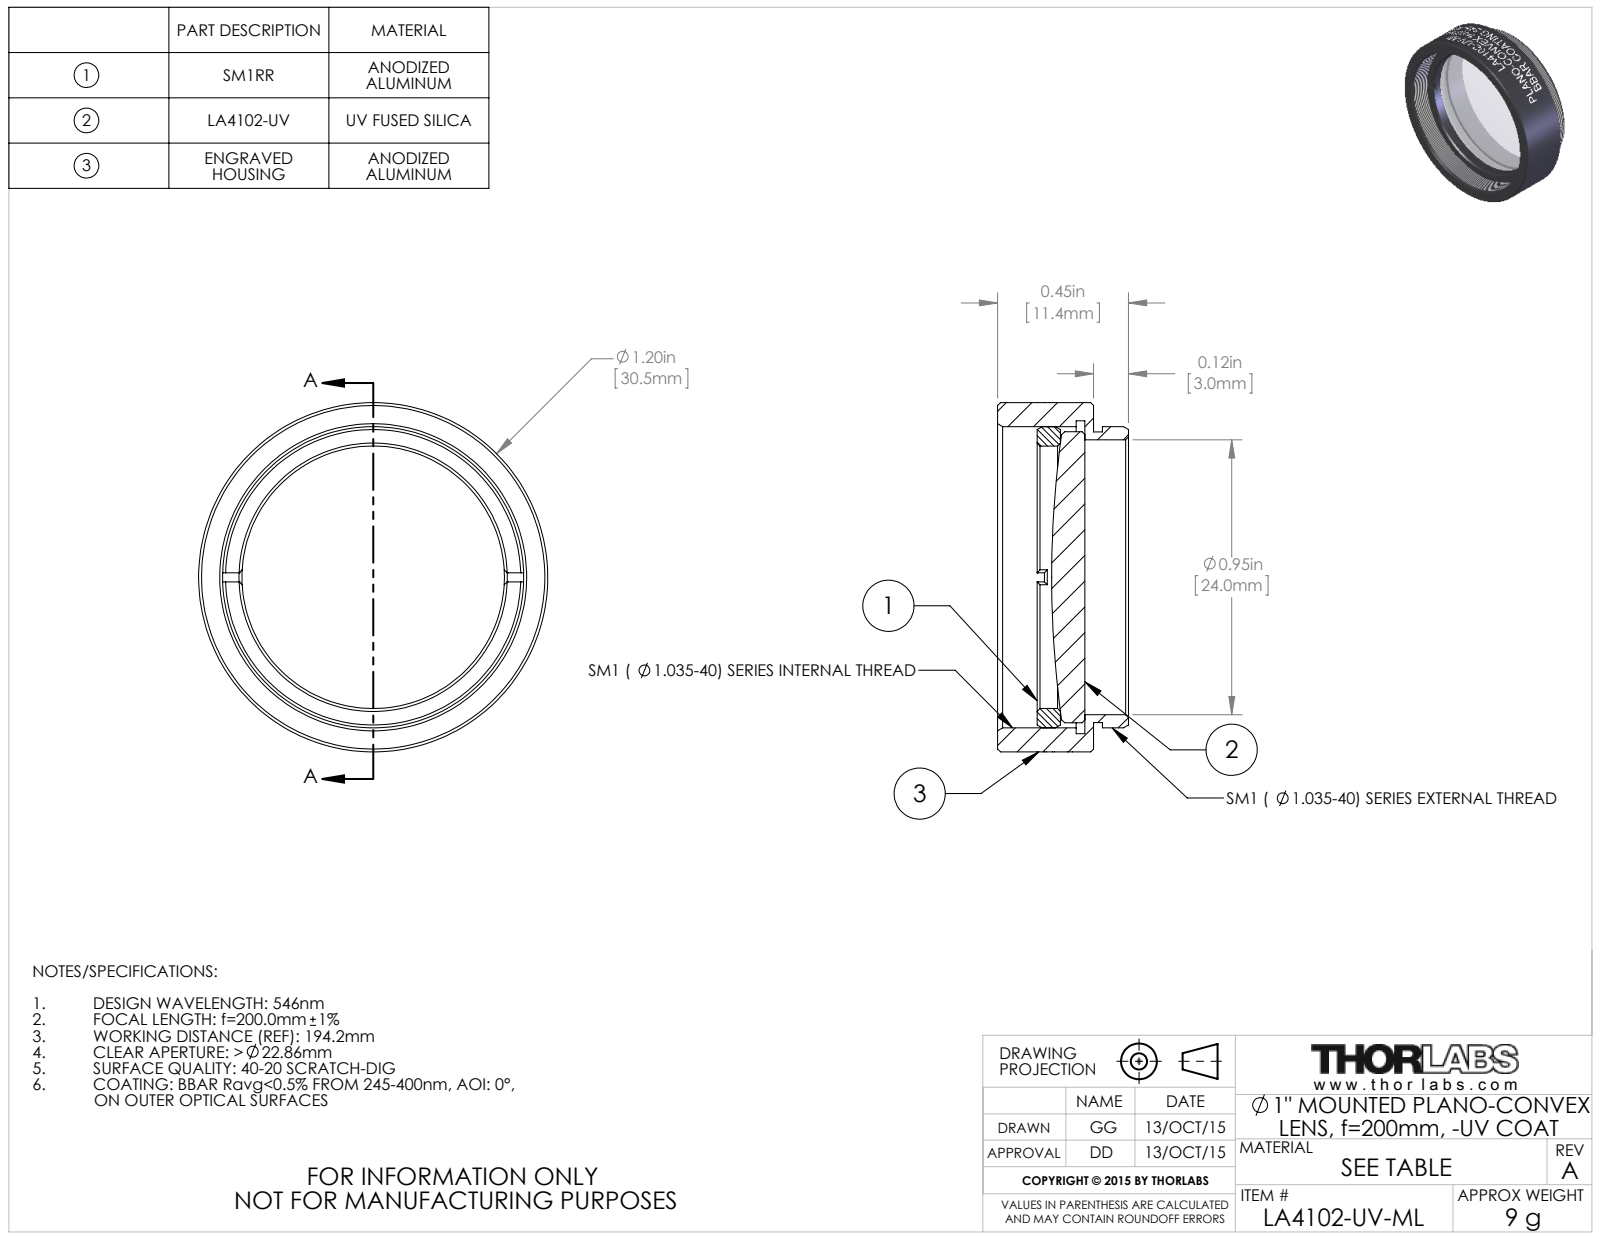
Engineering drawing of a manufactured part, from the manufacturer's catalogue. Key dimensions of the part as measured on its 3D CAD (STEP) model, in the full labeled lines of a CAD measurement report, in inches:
Part name (STEP PRODUCT): TTN039153-E0W
STEP written by: SolidWorks 2014 (CONFIG_CONTROL_DESIGN)
Units: inches
Bodies: 3 solids, 161 faces (20 planar, 113 cylindrical, 28 other)
Overall size (bounding box): 1.2 × 1.2 × 0.45
Volume: 0.202 in³ · Surface area: 6.654 in²
Round holes (diameter × count): ⌀0.902 ×1, ⌀0.945 ×1, ⌀1.075 ×1
Round bosses / shafts (diameter × count): ⌀1.2 ×1, ⌀1.035 ×1, ⌀1 ×1, ⌀0.999 ×1
Main face-to-face distances: 0.03, 0.33, 0.3, 0.114, 0.084, 0.216, 0.194, 0.164, 0.08, 0.136
